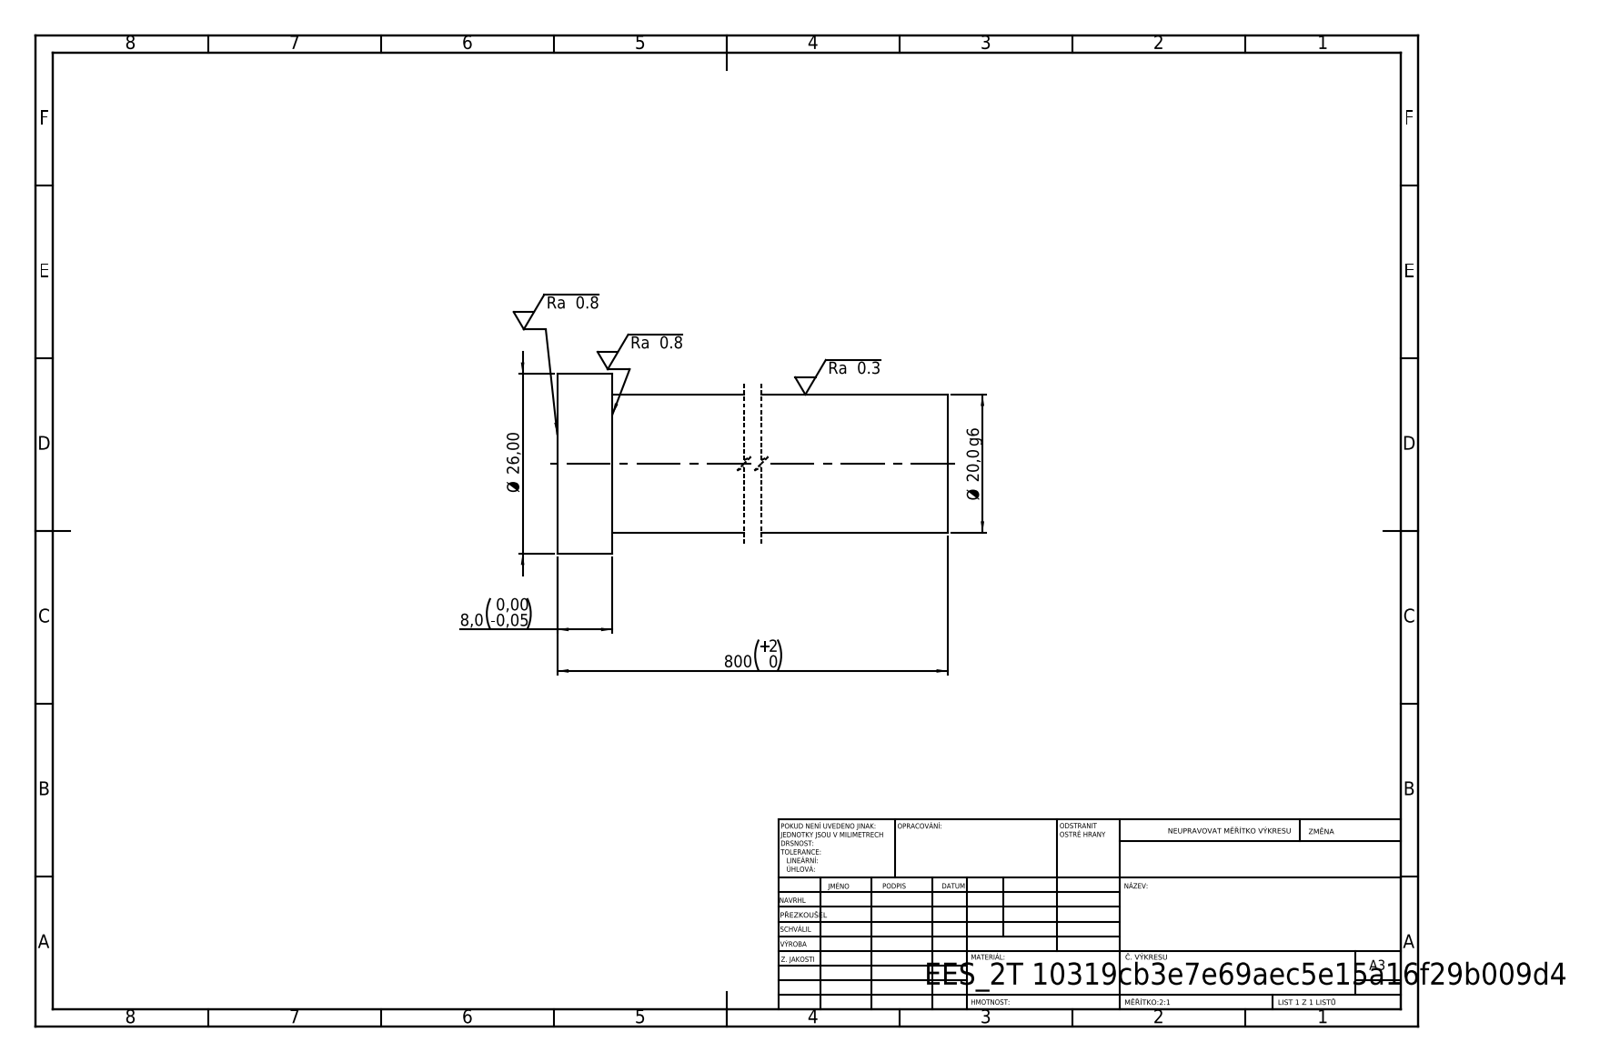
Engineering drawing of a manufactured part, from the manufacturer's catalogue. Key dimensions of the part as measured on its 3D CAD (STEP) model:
STEP written by: SolidWorks 2019 (CONFIG_CONTROL_DESIGN)
Units: millimetres
Bodies: 1 solid, 7 faces (3 planar, 4 cylindrical, 0 other)
Overall size (bounding box): 800 × 26 × 26
Volume: 253 062 mm³ · Surface area: 51 478 mm²
Round bosses / shafts (diameter × count): ⌀26 ×1, ⌀20 ×1
Main face-to-face distances: 800, 8, 792
